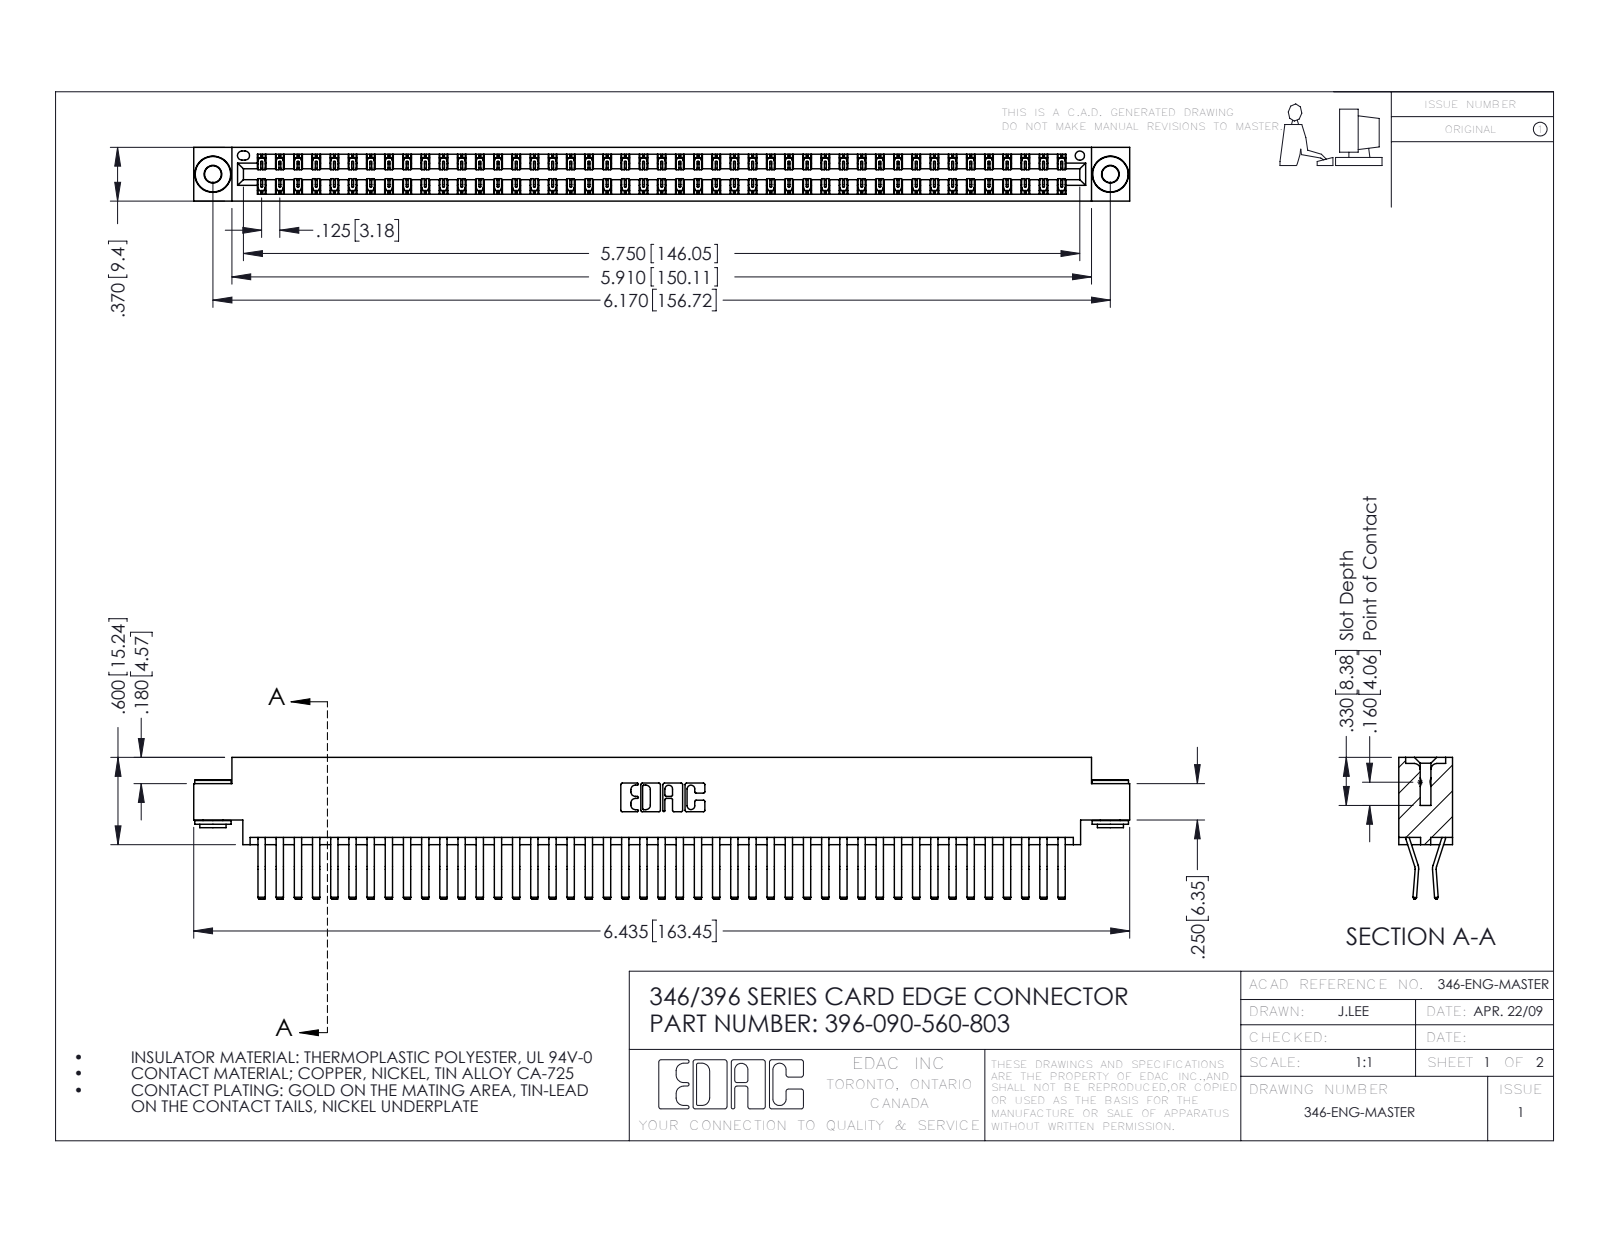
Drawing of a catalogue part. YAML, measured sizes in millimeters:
part_name: "345-292-001_560 Tail; 396-090-560-803; 346 Part_0.170 Offset - 0.156 Dia-TH; 345-250-002_345-250-002-102"
step_written_by: "SolidWorks 2016 (CONFIG_CONTROL_DESIGN)"
units: millimeters
bodies: {solids: 93, faces: 5024, planar: 3240, cylindrical: 1776, other: 8}
overall_size: [163.4, 24.8, 9.4]
volume: 16420
surface_area: 24580
round_holes:
  - {diameter: 2.9, count: 2}
  - {diameter: 4, count: 2}
  - {diameter: 1.6, count: 1}
round_bosses_or_shafts:
  - {diameter: 6.4, count: 2}
  - {diameter: 4.6, count: 2}
  - {diameter: 3.5, count: 2}
partial_cylinders:
  - {radius: 0.2, count: 135}
  - {radius: 0.3, count: 22}
  - {radius: 0.2, count: 6}
  - {radius: 0.8, count: 6}
  - {radius: 0.7, count: 3}
  - {radius: 0.3, count: 2}
  - {radius: 0.4, count: 2}
  - {radius: 0.6, count: 2}
face_to_face_distances: [1.2, 8.2, 9.4, 0.6, 6.4, 7, 1.8, 7.6, 3.8, 5.6]
hole_center_spacings: [6.2, 151.4, 156.7]
